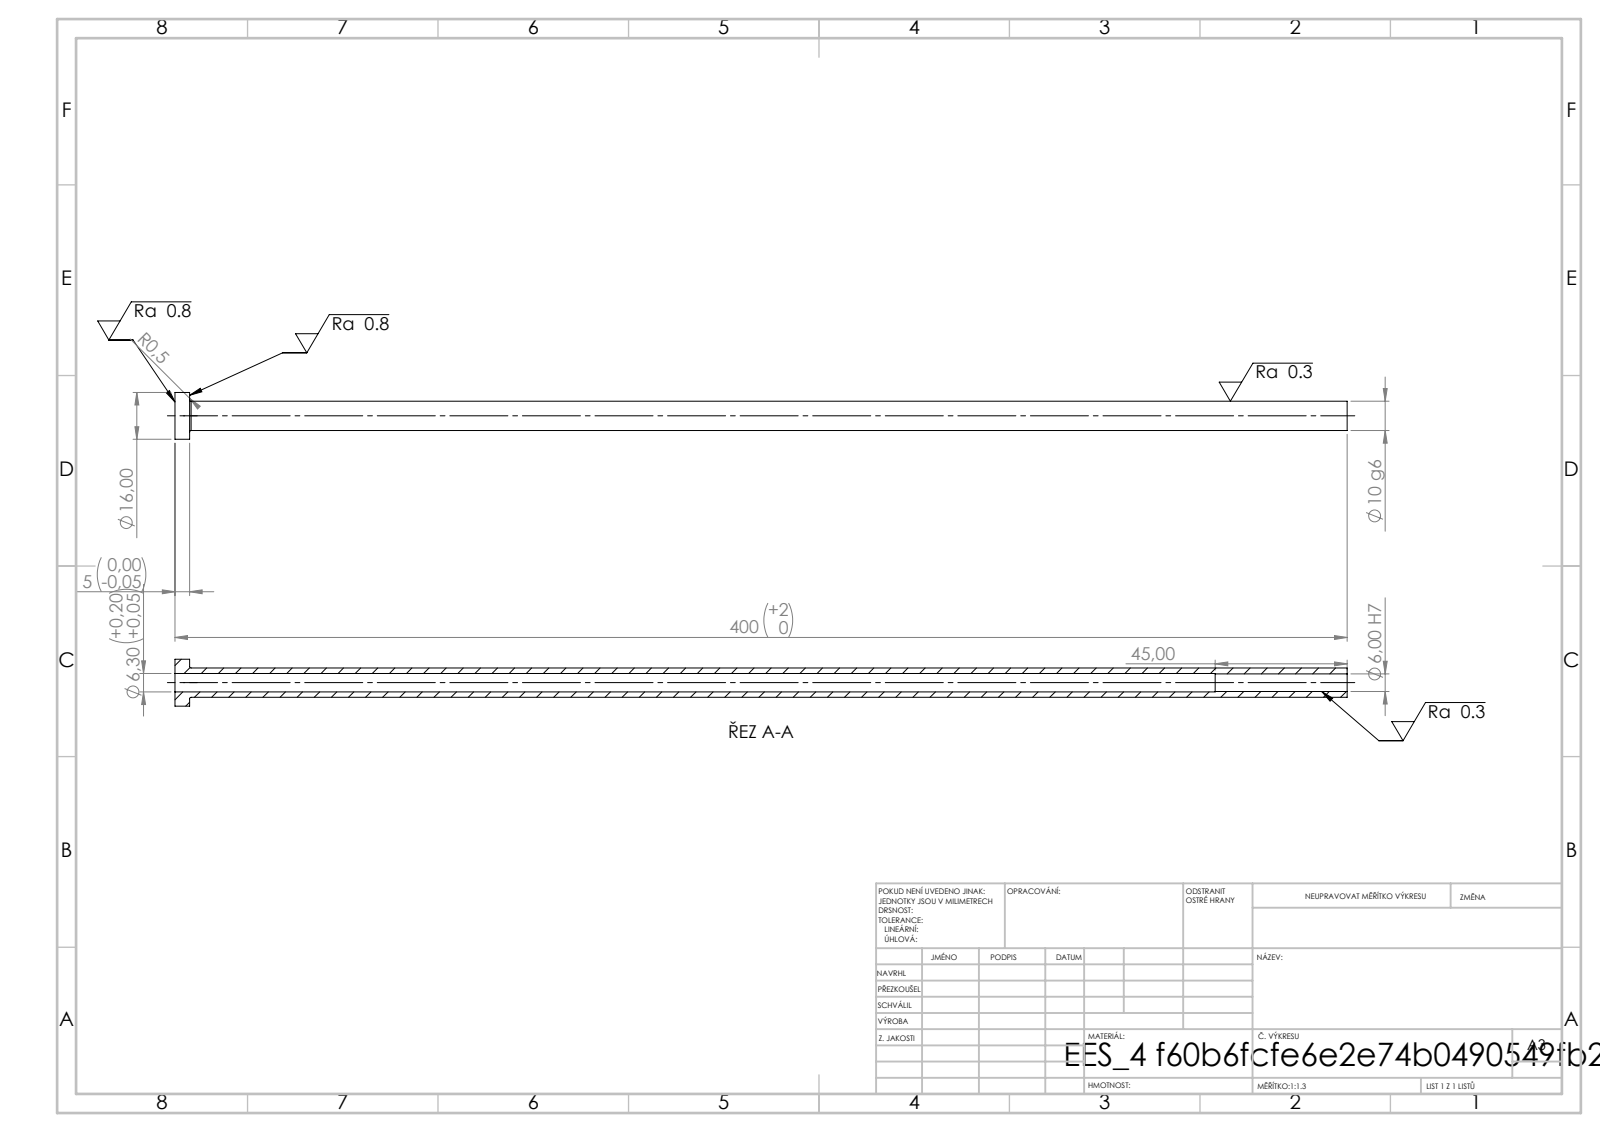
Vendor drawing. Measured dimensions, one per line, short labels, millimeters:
written by: SolidWorks 2019 (CONFIG_CONTROL_DESIGN)
unit: mm
bodies: 1 solid, 14 faces (4 planar, 8 cylindrical, 2 other)
size: 400 × 16 × 16
volume: 19 692 mm³; area: 20 874 mm²
holes: 1× ⌀6, 1× ⌀6.3
bosses: 1× ⌀16, 1× ⌀10
face distances: 5, 400, 395, 355, 350, 45
